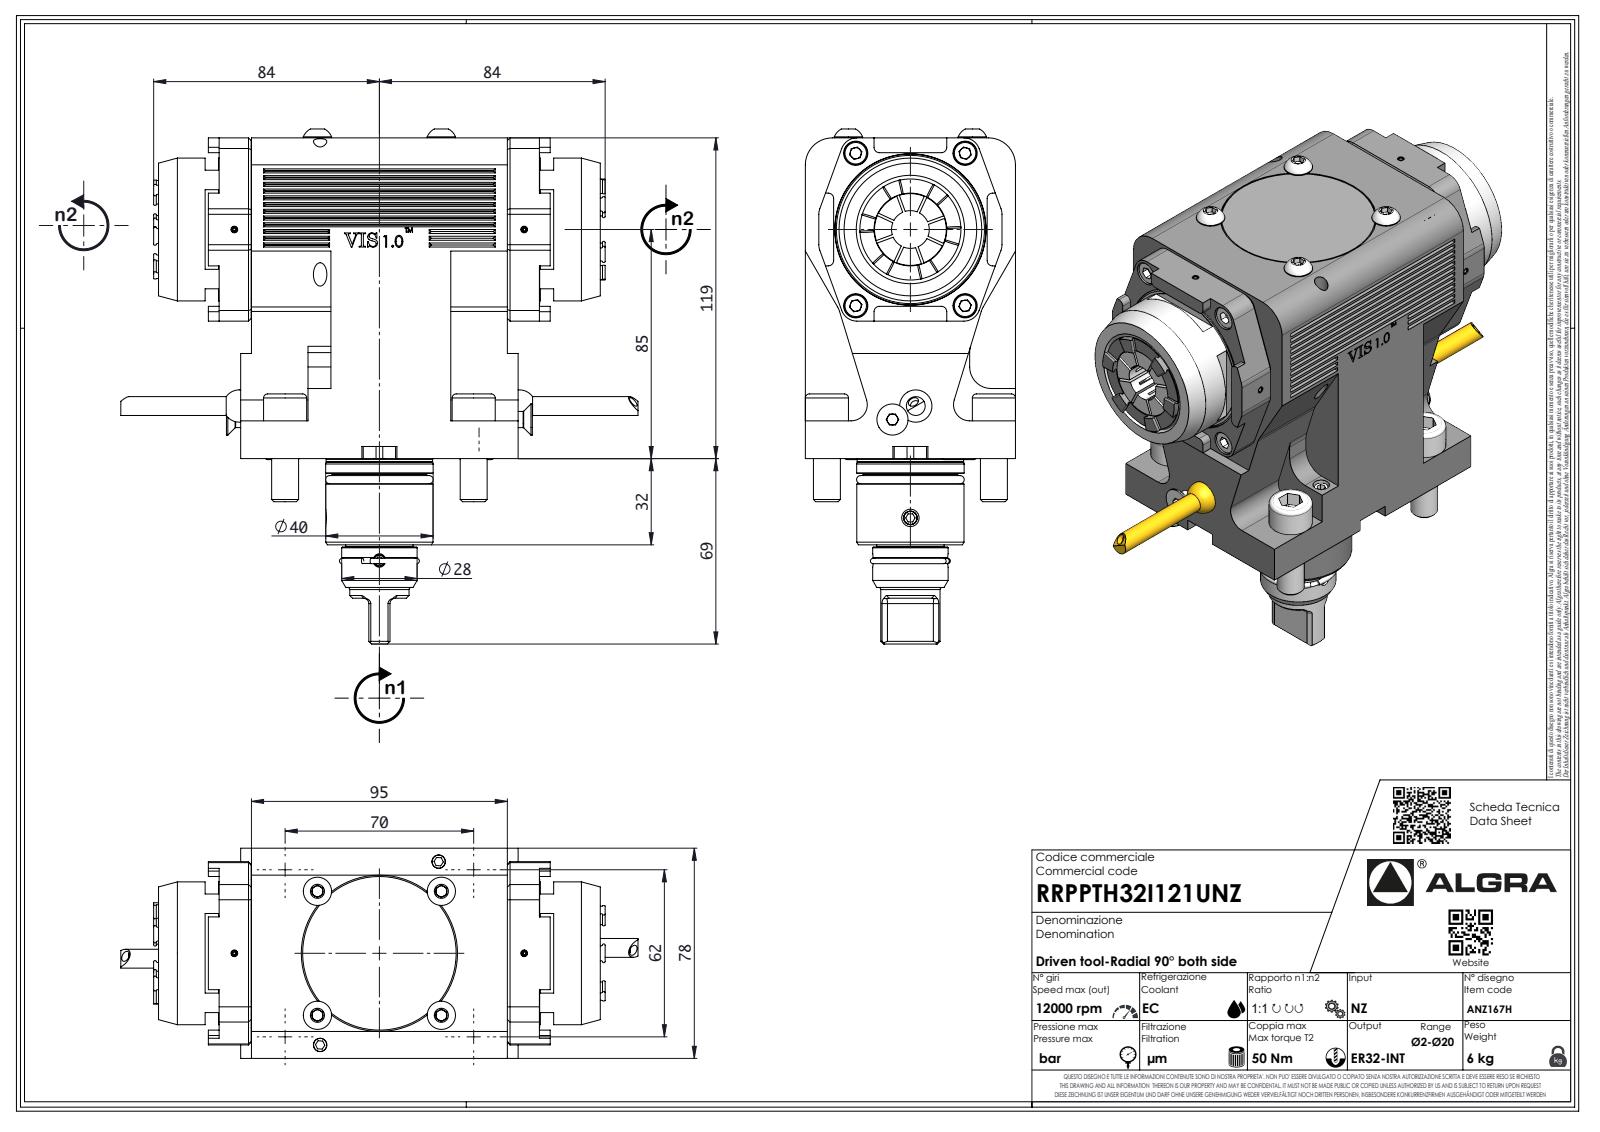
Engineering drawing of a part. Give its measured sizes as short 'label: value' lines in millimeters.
name: RRPPTH32I121UNZ
written by: SolidWorks 2023 (AUTOMOTIVE_DESIGN)
unit: mm
bodies: 1 solid, 736 faces (426 planar, 144 cylindrical, 166 other)
size: 192 × 187.8 × 78
volume: 1 067 000 mm³; area: 92 944 mm²
holes: 2× ⌀4, 1× ⌀2.1, 1× ⌀6
bosses: 4× ⌀16, 4× ⌀10, 2× ⌀7, 1× ⌀58.91, 1× ⌀53, 1× ⌀39.9, 1× ⌀39.8, 1× ⌀39.5
rounds: 16× R2, 16× R5, 10× R6, 7× R0.33, 7× R0.52, 7× R3.7, 6× R8, 2× R10
face distances: 78, 119, 4, 34.5, 12, 30.5, 129.5, 133.5, 99, 25
